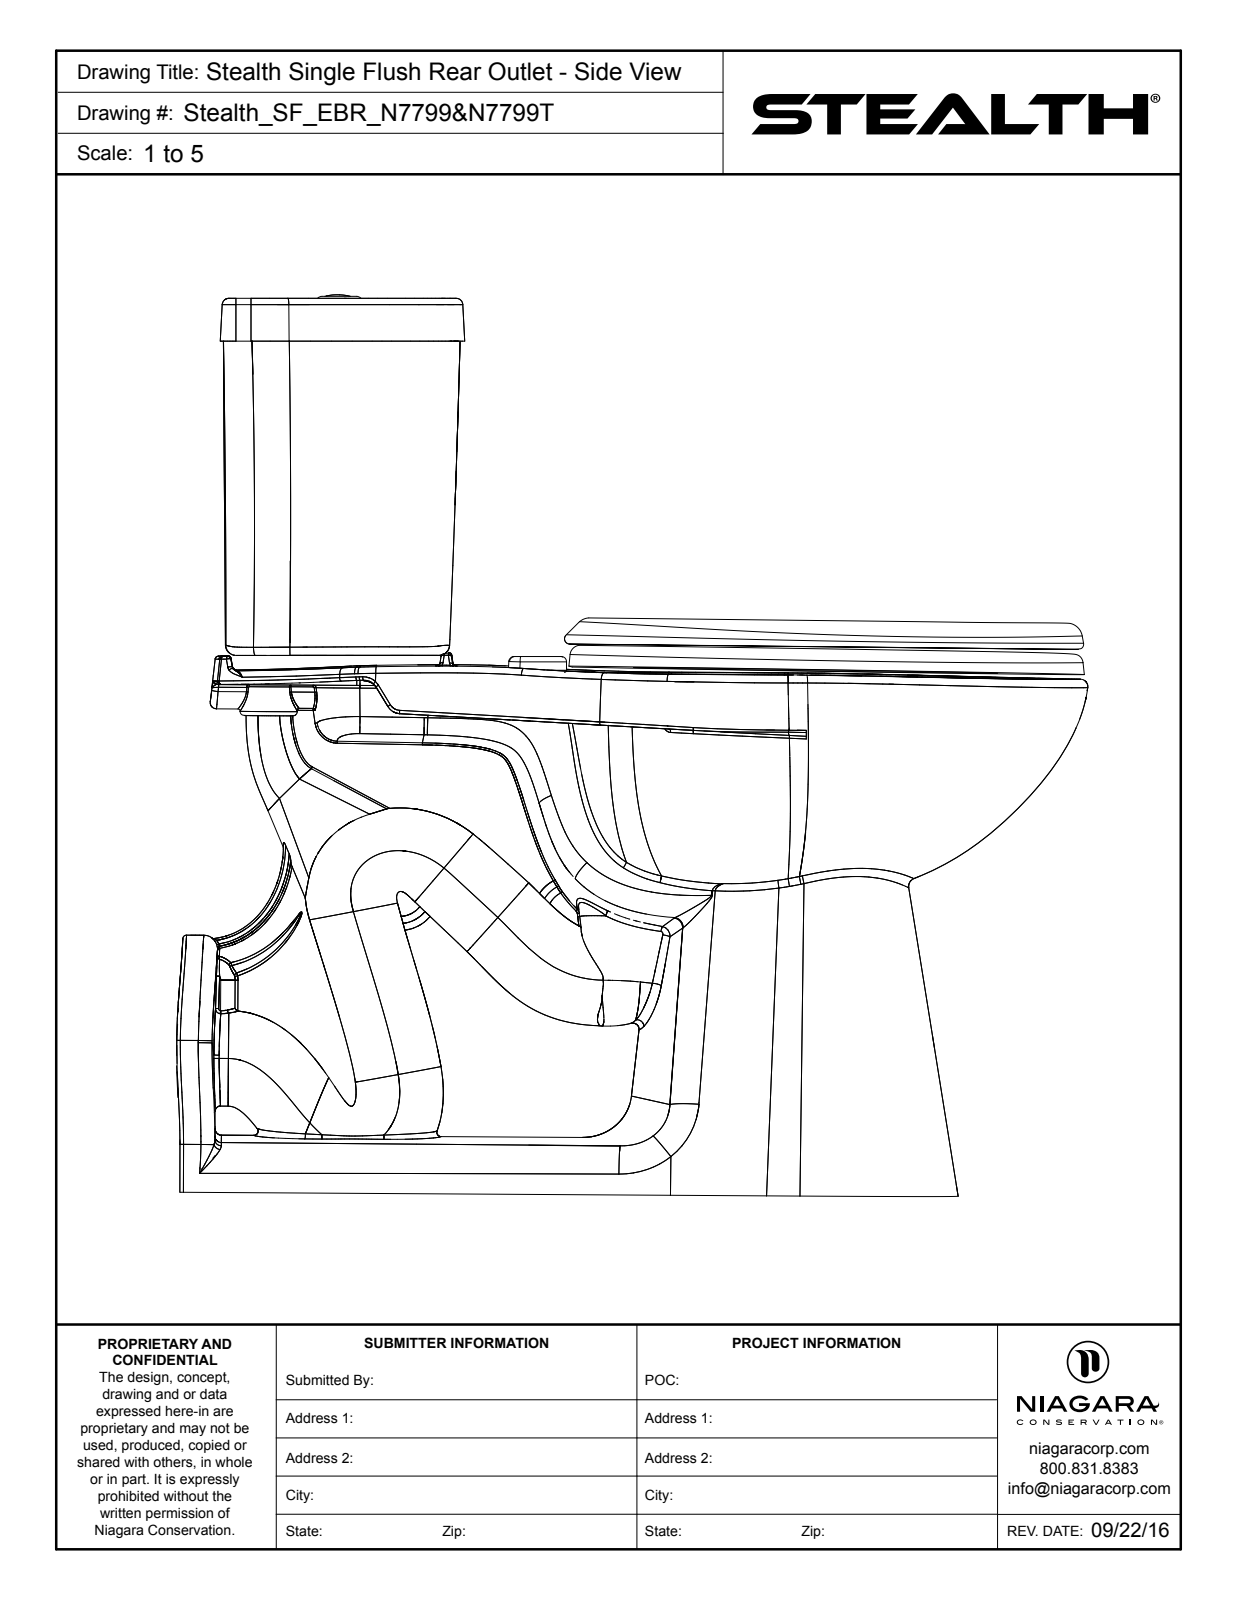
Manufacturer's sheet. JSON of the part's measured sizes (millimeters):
{"part_name": "N8531; N8496; N8291; N8071 (+8 more)", "step_written_by": "SolidWorks 2015 (CONFIG_CONTROL_DESIGN)", "units": "millimeters", "bodies": {"solids": 6, "faces": 1020, "planar": 73, "cylindrical": 39, "other": 908}, "overall_size": [863.7, 855.2, 468.1], "volume_mm3": 5749000, "surface_area_mm2": 3059000, "round_holes": [[2, 2], [27, 1], [31, 1]], "round_bosses_or_shafts": [[4, 2], [31, 1]], "partial_cylinders_radius": [[2, 6], [3, 4], [5, 3], [6.4, 3], [14, 2], [15, 2], [10, 1], [54, 1]], "face_to_face_distances": [25, 40.6, 20, 298, 338.7, 11.9, 286.2, 326.8, 9, 9.1], "hole_center_spacings": [10.8, 10.8, 21.6]}
